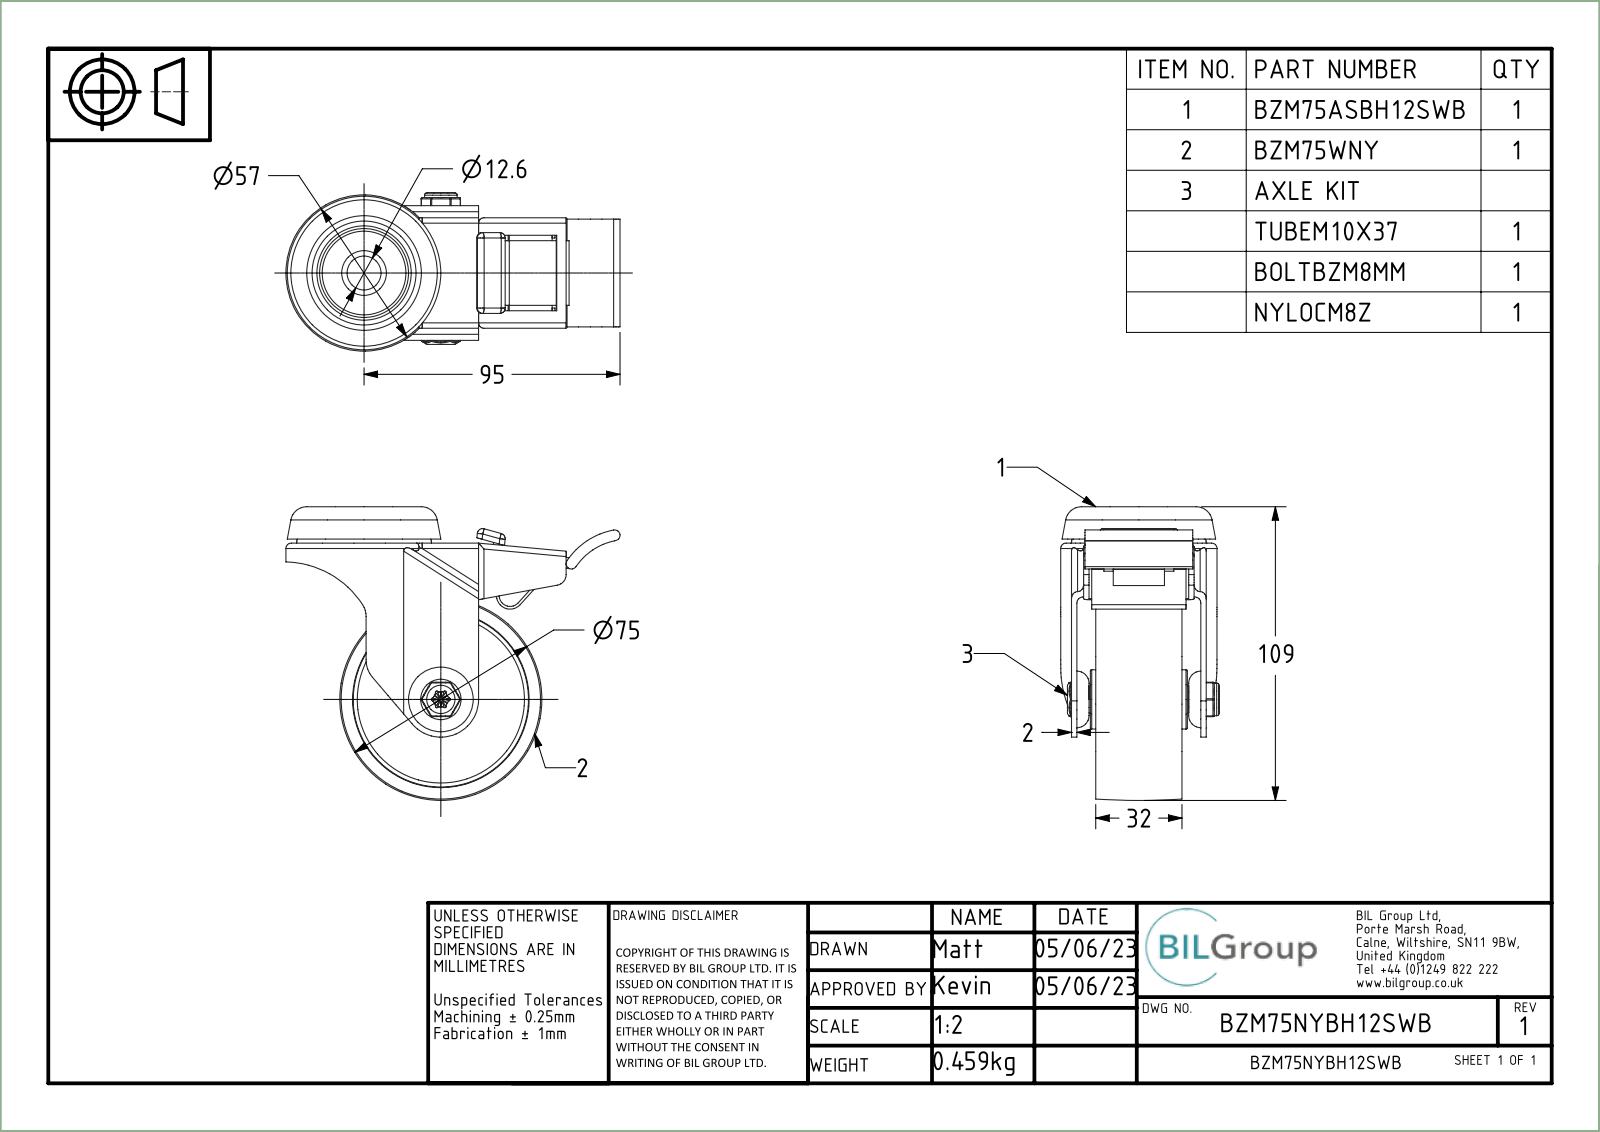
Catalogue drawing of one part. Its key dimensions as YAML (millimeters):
part_name: "BZM75ASBH12SWB; ZINC PLATED PRESSED STEEL HEAD; ZINC PLATED PRESSED STEEL FORKS; ZINC PLATED PRESSED STEEL BRAKE (+8 more)"
step_written_by: "Spatial InterOp 3D (CONFIG_CONTROL_DESIGN)"
units: millimeters
bodies: {solids: 10, faces: 611, planar: 211, cylindrical: 258, other: 142}
overall_size: [124, 109, 58.75]
volume: 114791
surface_area: 76157
round_holes:
  - {diameter: 8, count: 1}
  - {diameter: 8.2, count: 1}
  - {diameter: 8.3, count: 1}
  - {diameter: 8.6, count: 1}
  - {diameter: 10.2, count: 1}
  - {diameter: 12.6, count: 1}
  - {diameter: 30, count: 1}
round_bosses_or_shafts:
  - {diameter: 48, count: 1}
  - {diameter: 22, count: 1}
  - {diameter: 12.1, count: 1}
  - {diameter: 10, count: 1}
  - {diameter: 6, count: 1}
partial_cylinders:
  - {radius: 2, count: 36}
  - {radius: 0.5, count: 30}
  - {radius: 2.25, count: 8}
  - {radius: 1, count: 7}
  - {radius: 4, count: 3}
  - {radius: 1.75, count: 2}
  - {radius: 3, count: 2}
  - {radius: 2.75, count: 1}
face_to_face_distances: [2, 4.5, 4, 2.5, 43.5, 39, 41, 18, 6.5, 21]
